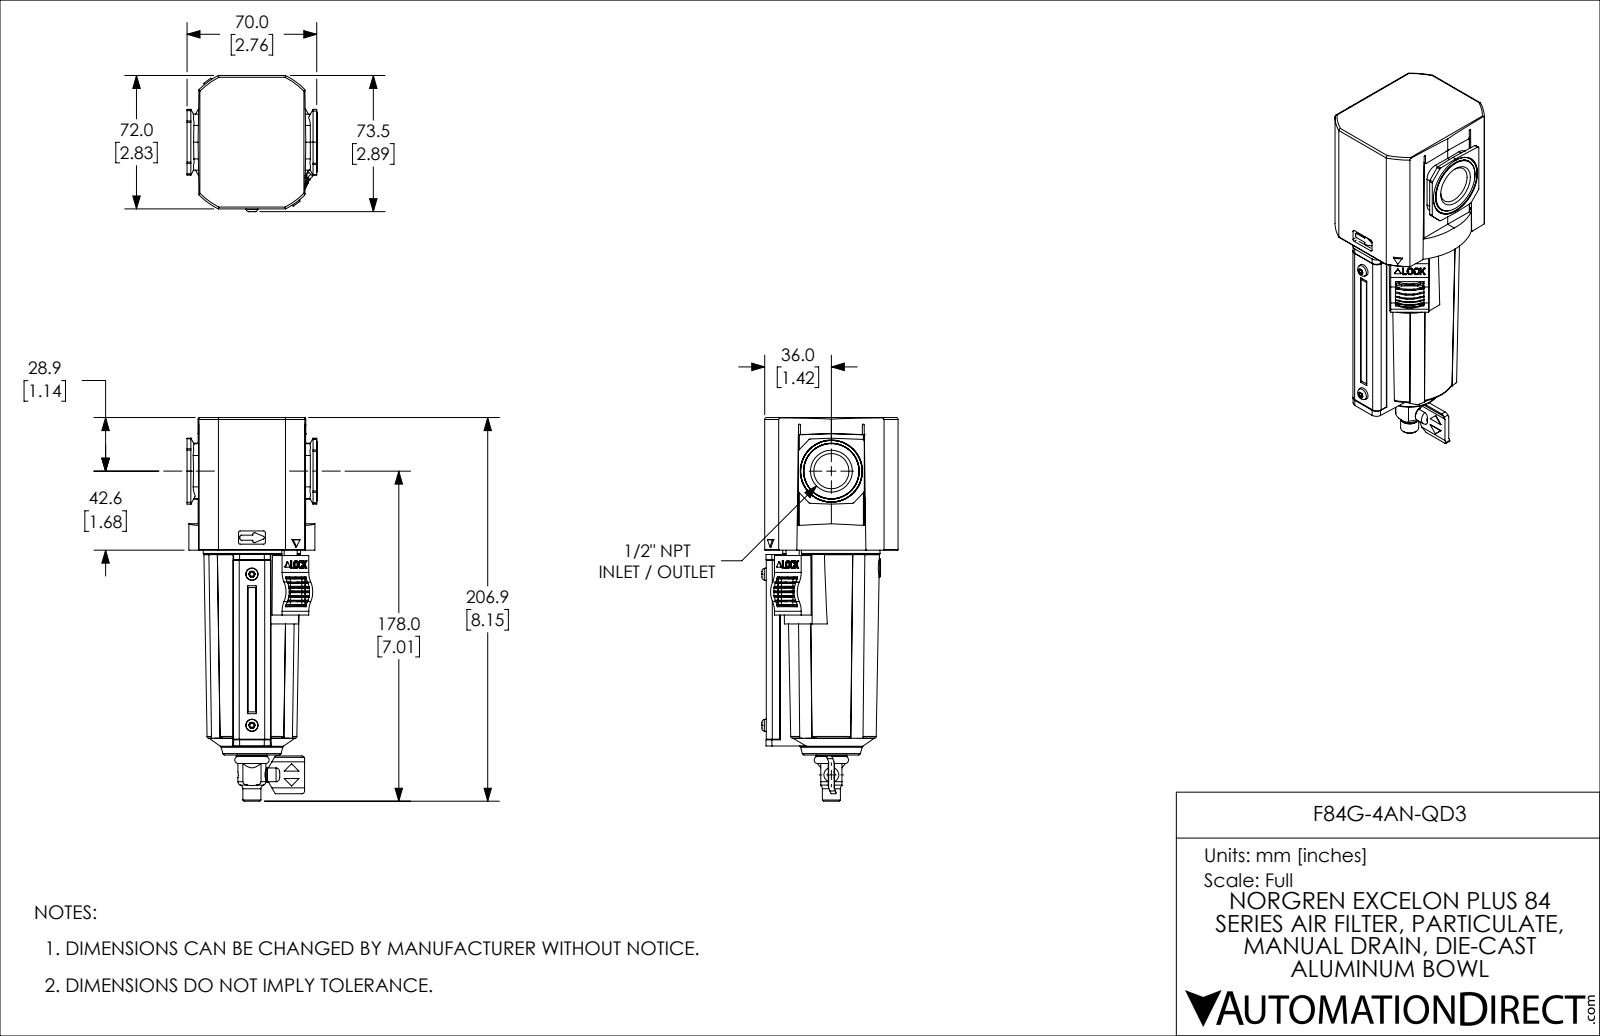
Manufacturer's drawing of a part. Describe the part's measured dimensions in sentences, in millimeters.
The part is named "F84G-4AN-QD3". Its 3-D file was written by "SolidWorks 2021 (CONFIG_CONTROL_DESIGN)". It is 6 solids with 1221 faces: 529 planar, 430 cylindrical and 262 other. Overall it measures 206.9 by 73.5 by 70.3 millimeters. Its volume is 465 700 cubic millimeters and its surface area 108 400 square millimeters. Round holes: 2 of diameter 2.8, 2 of diameter 4.1, 1 of diameter 3.1, 1 of diameter 3.2, 1 of diameter 6, 1 of diameter 6.4, 1 of diameter 9.5, 1 of diameter 16.1, 1 of diameter 62.5. Round bosses or shafts: 3 of diameter 8, 2 of diameter 7, 2 of diameter 5.4, 1 of diameter 53.9, 1 of diameter 52.5, 1 of diameter 51.3, 1 of diameter 49.8, 1 of diameter 49.6. Partial cylindrical surfaces (rounded edges, fillets, slot ends): 47 of radius 1, 37 of radius 0.5, 28 of radius 0.7, 18 of radius 0.3, 8 of radius 0.2, 8 of radius 1, 8 of radius 1.1, 8 of radius 1.5. The main face-to-face distances are 1.5, 59.7, 61.2, 52, 9.6, 62.4, 72, 9.2, 50.5, 70. The hole center spacings are 15.1, 30.2, 63.6.
